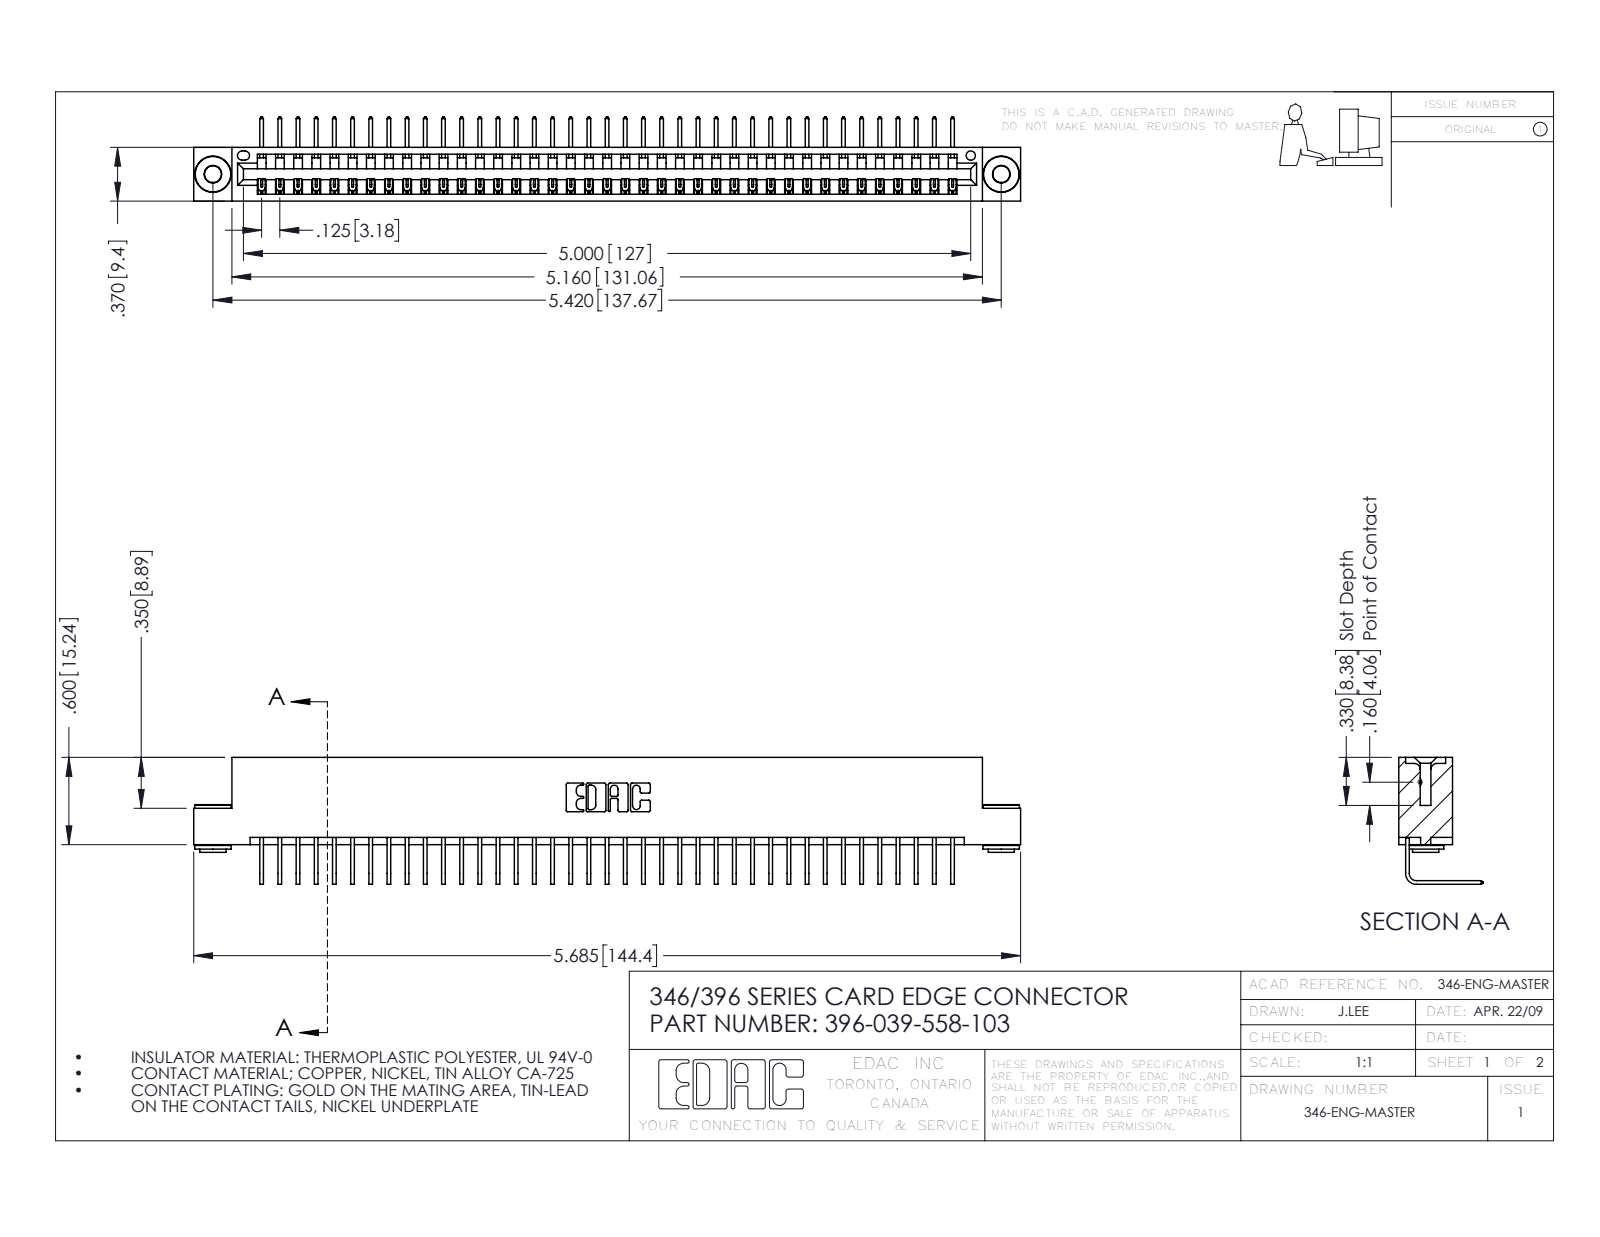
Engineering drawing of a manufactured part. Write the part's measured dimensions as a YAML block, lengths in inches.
part_name: "345-250-002_345-250-002-102; 346 Part_Flush Mounting Lugs - 0.156 Dia-TH; 396-039-558-103; 345-292-001_558 Tail - 2"
step_written_by: "SolidWorks 2016 (CONFIG_CONTROL_DESIGN)"
units: inches
bodies: {solids: 42, faces: 2500, planar: 1724, cylindrical: 768, other: 8}
overall_size: [5.685, 0.873, 0.58]
volume: 0.851
surface_area: 28.52
round_holes:
  - {diameter: 0.116, count: 2}
  - {diameter: 0.156, count: 2}
  - {diameter: 0.064, count: 1}
round_bosses_or_shafts:
  - {diameter: 0.25, count: 2}
  - {diameter: 0.18, count: 2}
  - {diameter: 0.136, count: 2}
partial_cylinders:
  - {radius: 0.006, count: 78}
  - {radius: 0.01, count: 22}
  - {radius: 0.007, count: 6}
  - {radius: 0.031, count: 6}
  - {radius: 0.026, count: 3}
  - {radius: 0.031, count: 2}
  - {radius: 0.04, count: 2}
  - {radius: 0.014, count: 1}
face_to_face_distances: [0.322, 0.048, 0.37, 0.25, 0.025, 0.298, 0.072, 0.148, 0.222, 0.1]
hole_center_spacings: [0.246, 5.211, 5.42]
